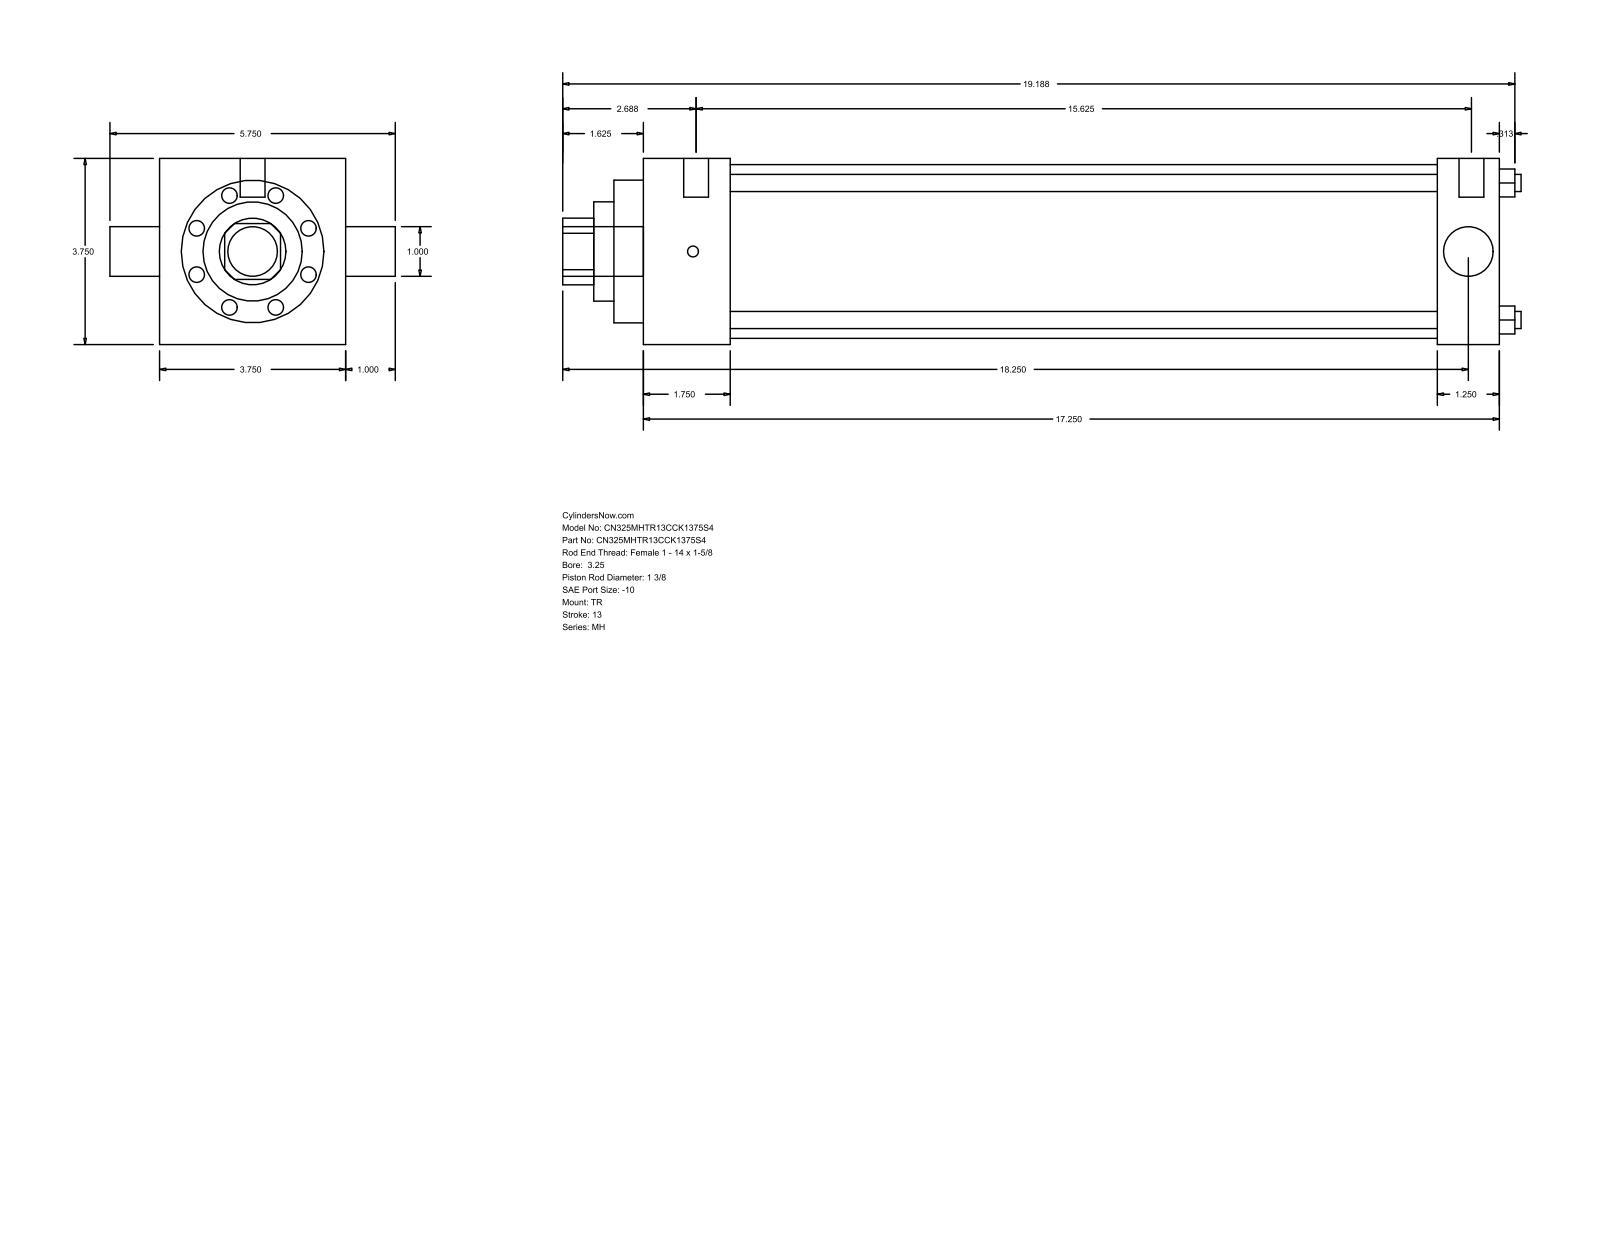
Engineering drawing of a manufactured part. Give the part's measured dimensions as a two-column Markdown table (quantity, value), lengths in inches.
| quantity | value |
| --- | --- |
| part name | MH_TR__0325_1.375 |
| STEP written by | GSSL Pune (CONFIG_CONTROL_DESIGN) |
| units | inches |
| bodies | 0 solids, 86 faces (61 planar, 25 cylindrical, 0 other) |
| overall size | 19.313 × 5.75 × 3.75 |
| round holes (diameter × count) | 0.345 × 4, 1 × 1, 1.375 × 1, 2 × 1, 2.875 × 1, 3.5 × 1 |
| round bosses / shafts (diameter × count) | 0.219 × 3, 0.5 × 2, 1 × 1 |
| partial cylindrical surfaces (radius × count) | 0.672 × 1 |
| main face-to-face distances | 3.75, 17.25, 1.75, 16, 14.25, 15.5, 1.25, 0.594, 2.344, 16.594 |
| hole center spacings | 1.952, 2.76, 3.903 |
